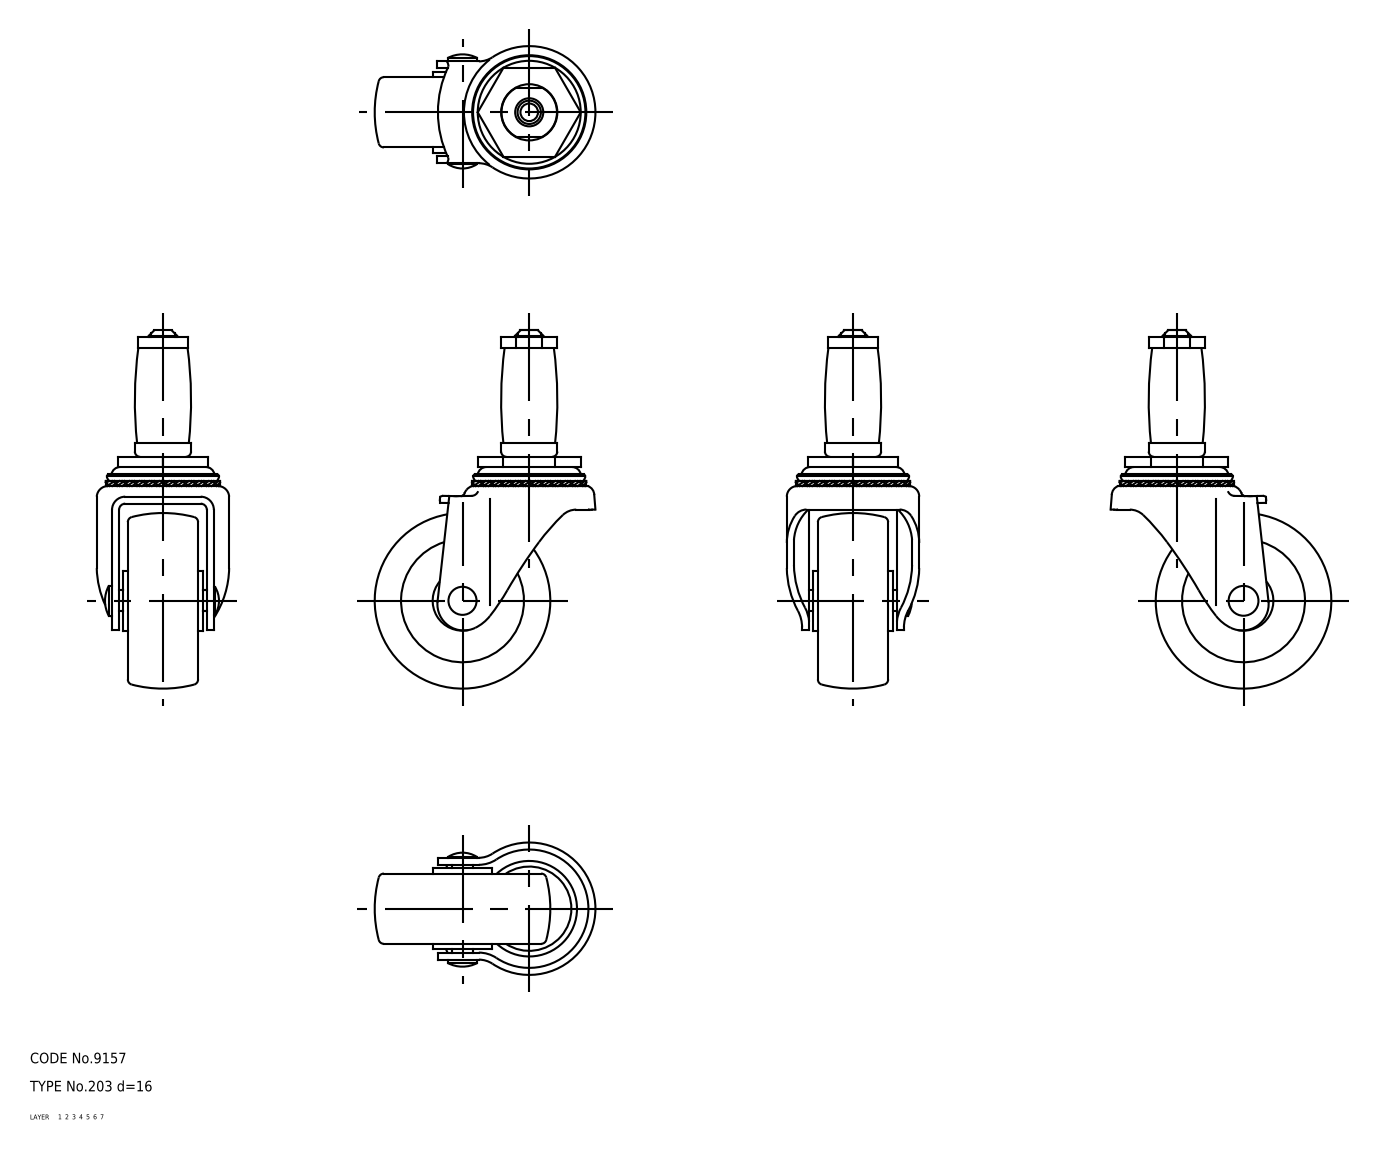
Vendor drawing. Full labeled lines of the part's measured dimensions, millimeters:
Part name (STEP PRODUCT): wheel; main shaft; axle; No_203_d16_21242_36
STEP written by: CADfix (AUTOMOTIVE_DESIGN)
Units: millimetres
Bodies: 4 solids, 185 faces (0 planar, 0 cylindrical, 185 other)
Overall size (bounding box): 102 × 62.85 × 37.7
Volume: 56 346 mm³ · Surface area: 19 800 mm²
